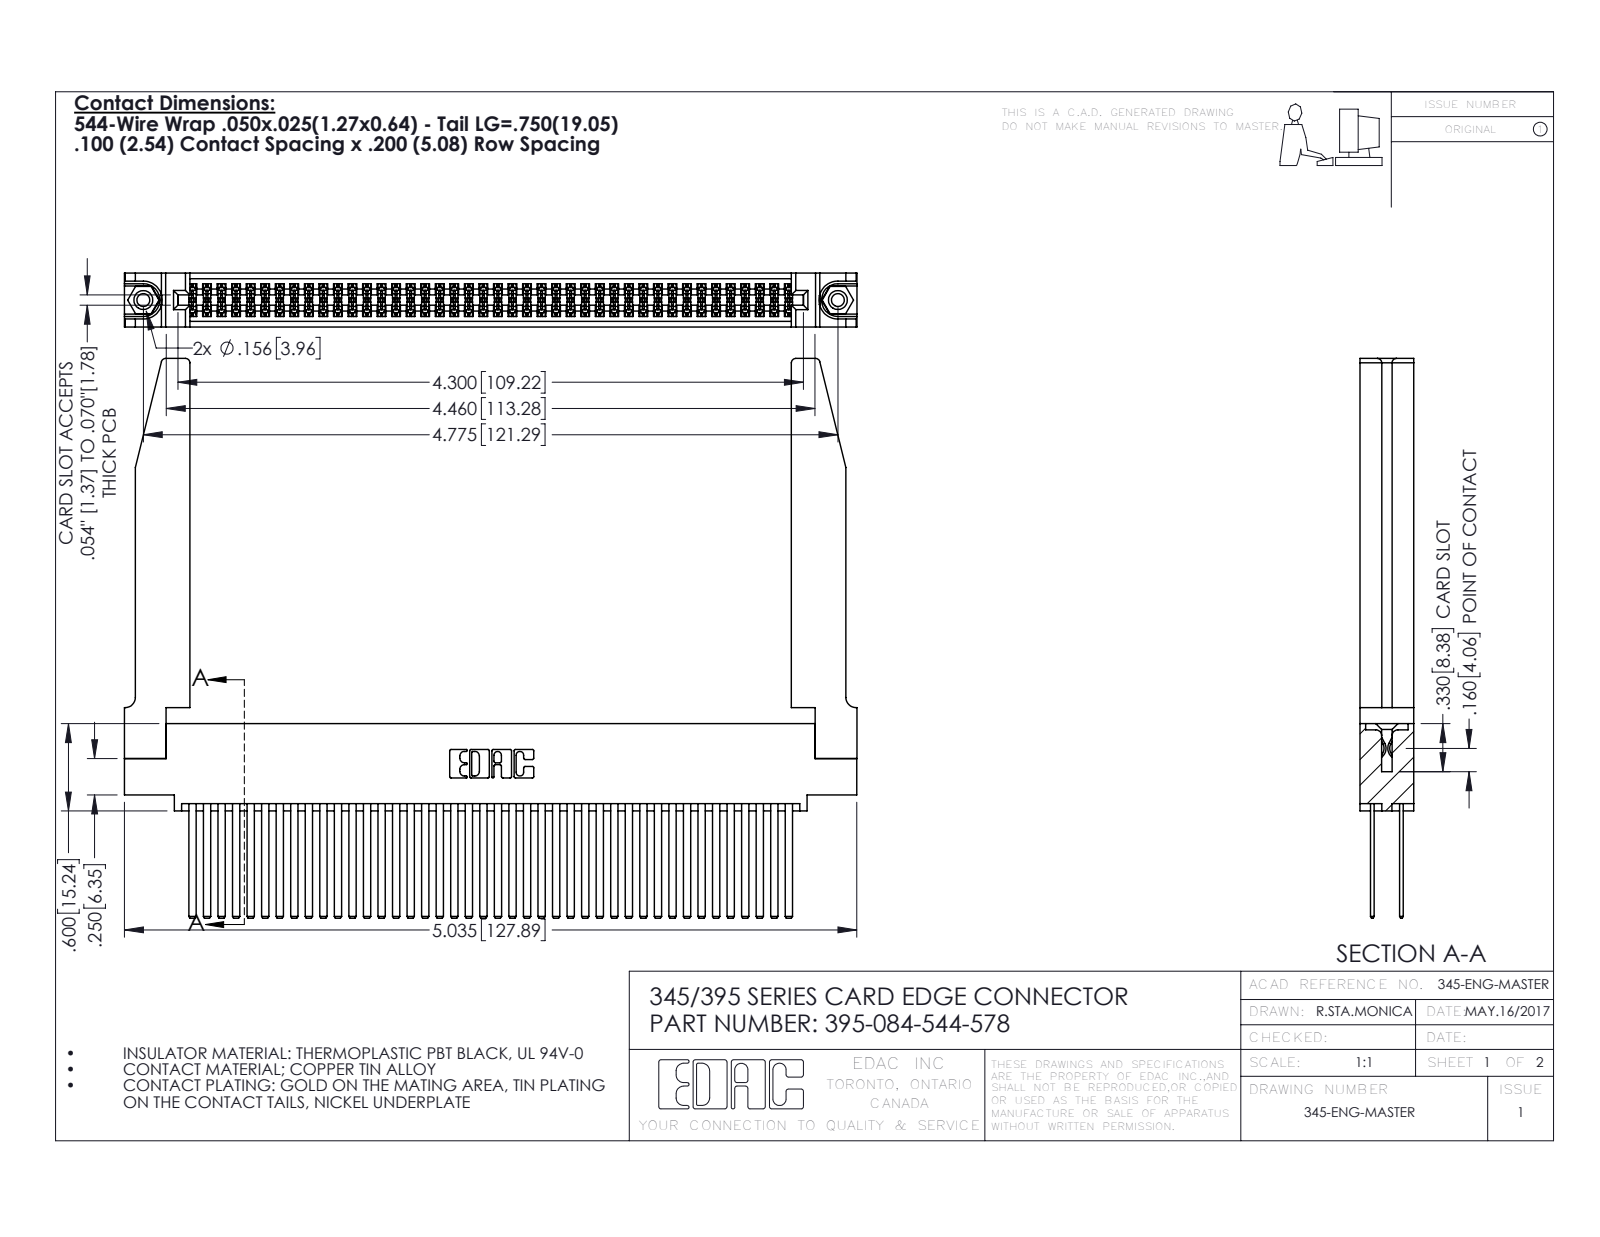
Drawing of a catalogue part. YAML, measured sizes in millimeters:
part_name: "345-250-001_345-250-001-102; 345 Part_0.110 Offset - 0.156 Dia-TH; 345-292-001_345-293-144; 345-220-078_345-220-078 (+1 more)"
step_written_by: "SolidWorks 2016 (CONFIG_CONTROL_DESIGN)"
units: millimeters
bodies: {solids: 89, faces: 4060, planar: 2662, cylindrical: 1346, other: 52}
overall_size: [127.9, 97.7, 9.4]
volume: 21300
surface_area: 30380
round_holes:
  - {diameter: 2.3, count: 2}
  - {diameter: 3.2, count: 2}
  - {diameter: 4, count: 2}
  - {diameter: 1.6, count: 1}
round_bosses_or_shafts:
  - {diameter: 3.9, count: 2}
partial_cylinders:
  - {radius: 0.2, count: 126}
  - {radius: 0.3, count: 22}
  - {radius: 0.8, count: 8}
  - {radius: 0.2, count: 6}
  - {radius: 0.8, count: 6}
  - {radius: 0.7, count: 3}
  - {radius: 0.4, count: 2}
  - {radius: 0.5, count: 2}
face_to_face_distances: [1.8, 7.6, 2.5, 6.9, 0.6, 5.1, 9.4, 5.7, 4.4, 3.8]
hole_center_spacings: [6.9, 115.3, 121.3]
